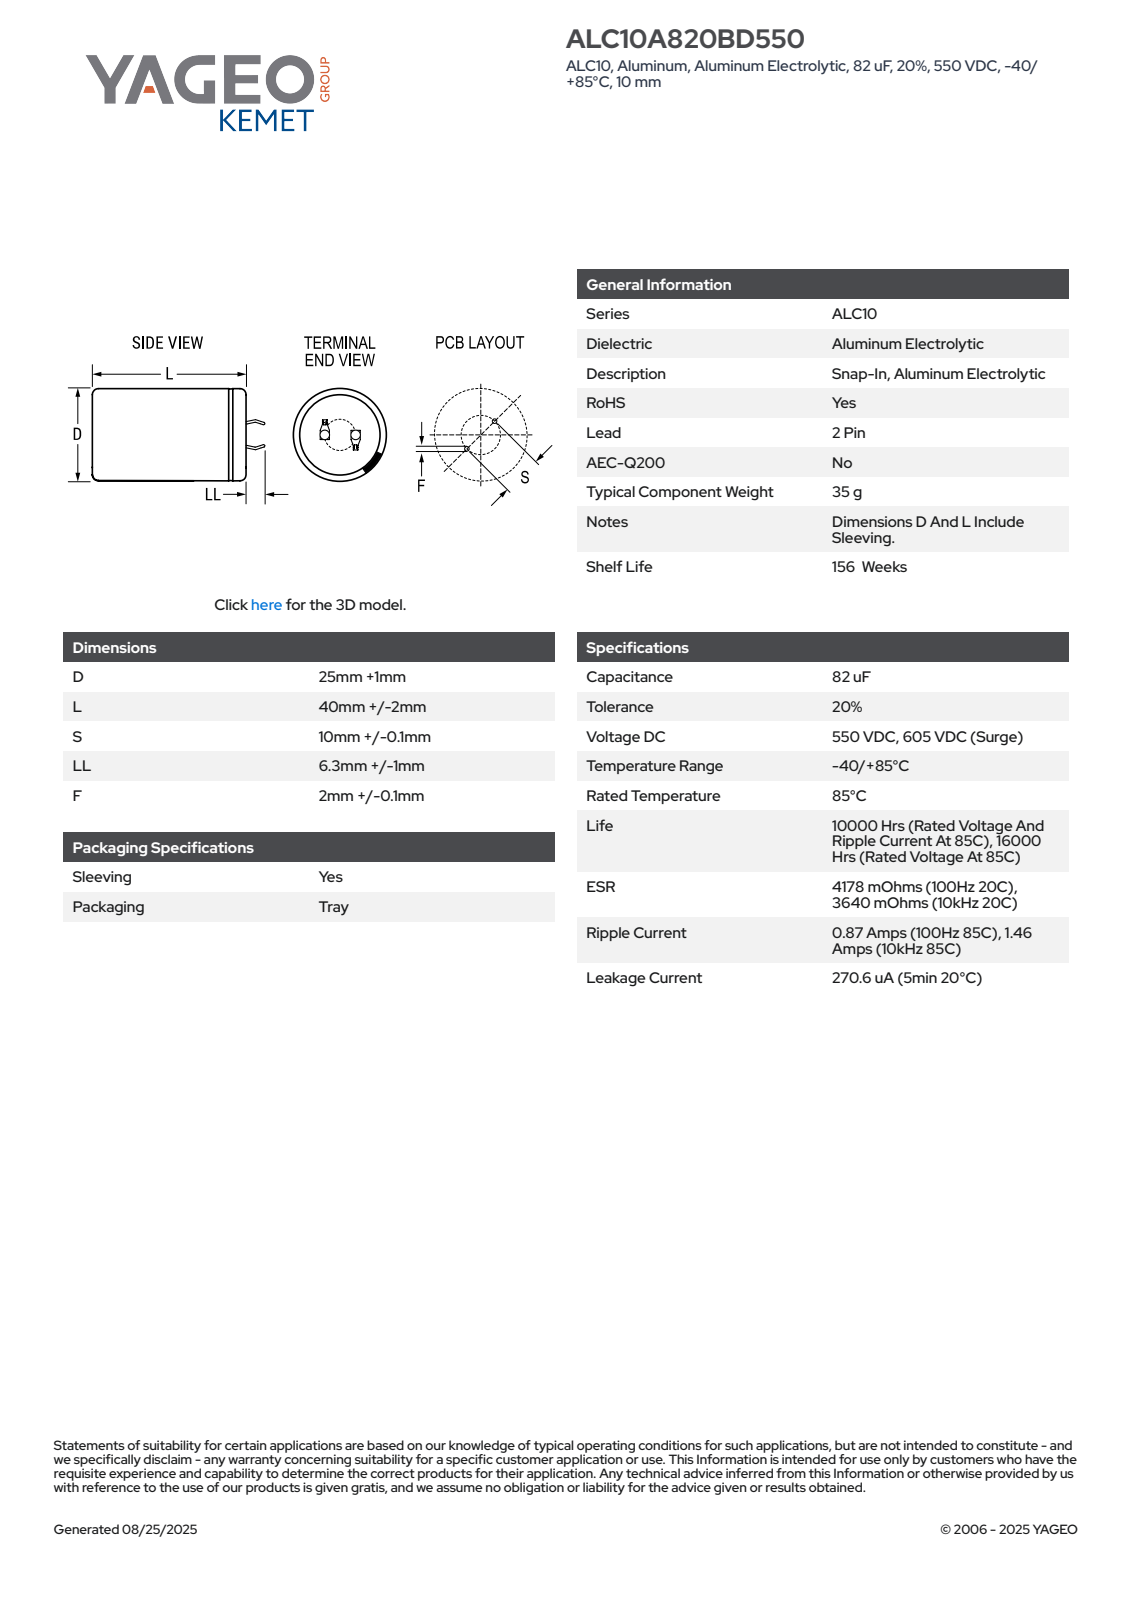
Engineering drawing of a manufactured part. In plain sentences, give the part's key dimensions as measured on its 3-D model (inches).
The part is named "CARS_K2P_25X40_D26L42S10LL7.3F2.1". Its 3-D file was written by "SolidWorks 2014 (AUTOMOTIVE_DESIGN)". It is 1 solid with 100 faces: 52 planar, 9 cylindrical and 39 other. Overall it measures 1.941 by 1.024 by 1.024 inches. Its volume is 1.349 cubic inches and its surface area 6.997 square inches. Round holes: 1 of diameter 0.906. Round bosses or shafts: 1 of diameter 1.024. Partial cylindrical surfaces (rounded edges, fillets, slot ends): 1 of radius 0.511. The main face-to-face distances are 1.653, 0.024, 1.673, 0.02, 0.279, 0.301, 0.03, 0.053, 0.302, 0.255.
